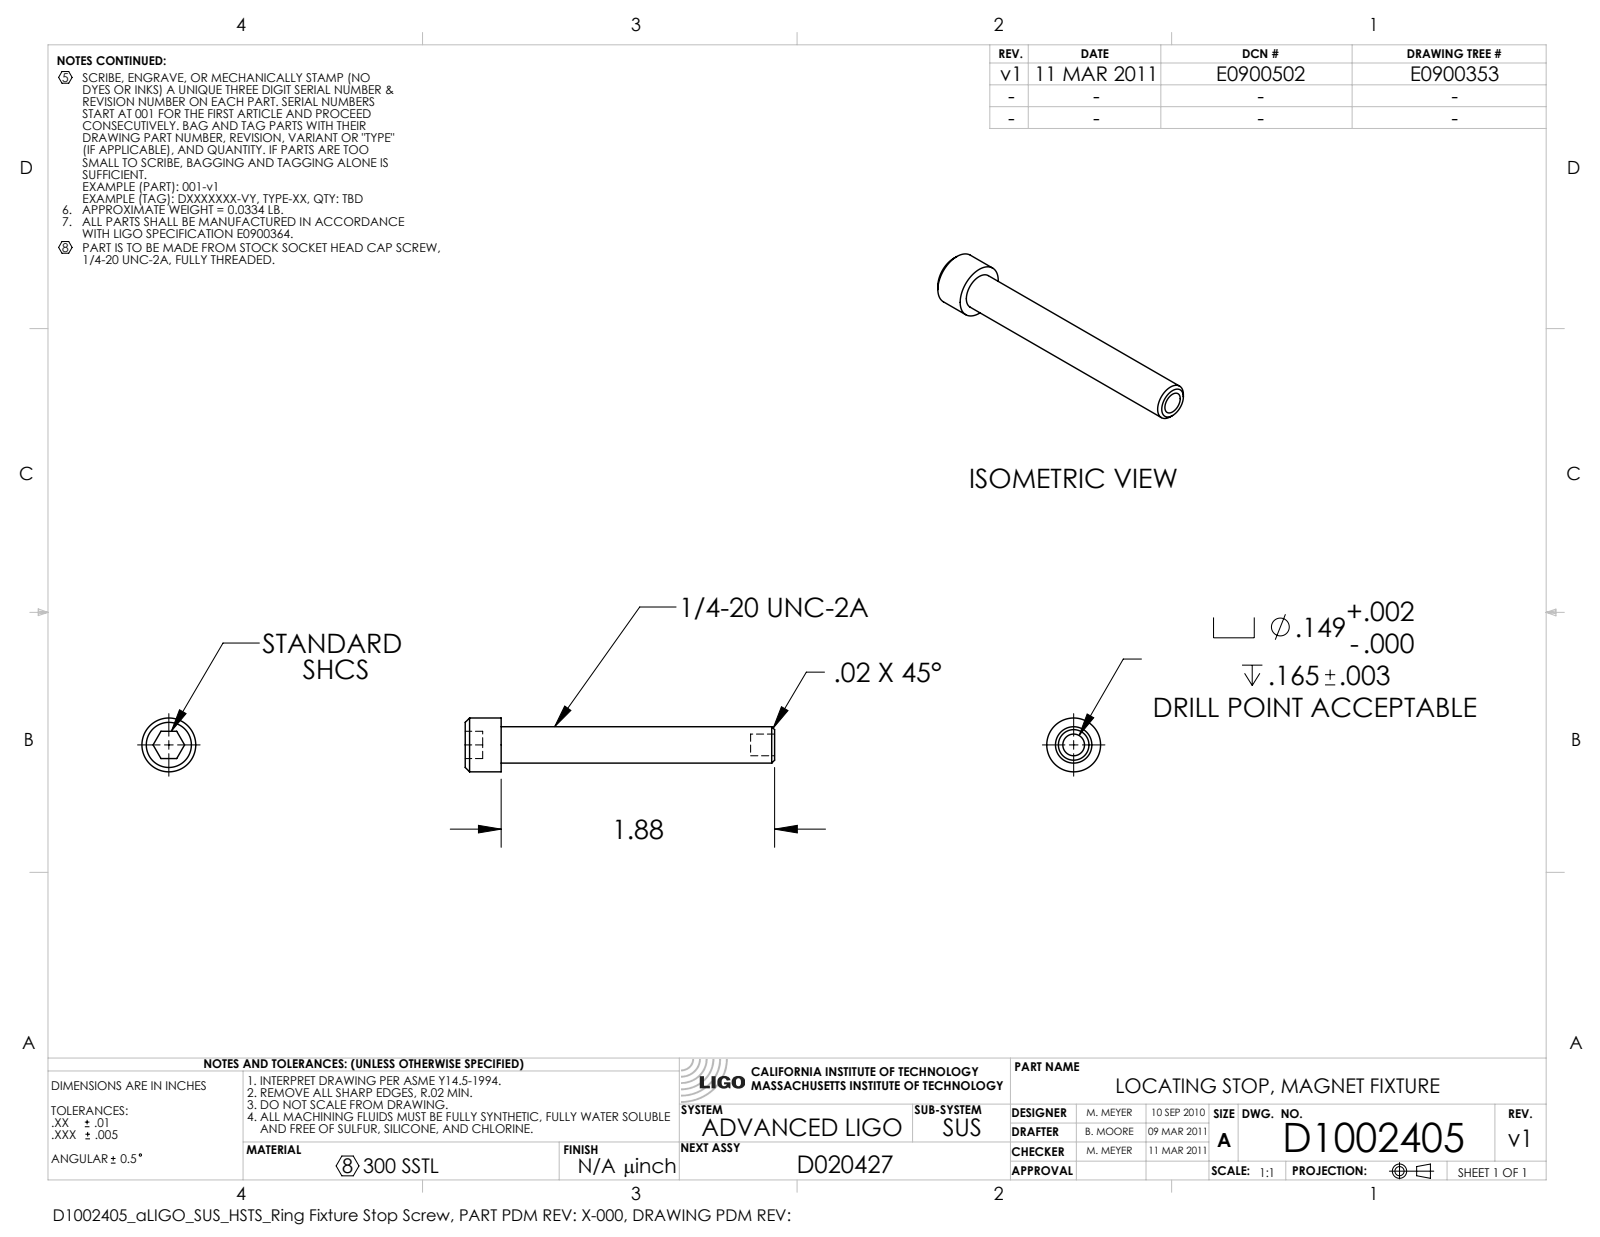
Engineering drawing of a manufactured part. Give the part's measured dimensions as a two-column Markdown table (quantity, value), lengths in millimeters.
| quantity | value |
| --- | --- |
| part name | D1002405-v1_aLIGO_SUS_HSTS_Ring Fixture Stop Screw |
| STEP written by | SolidWorks 2010 (AUTOMOTIVE_DESIGN) |
| units | millimeters |
| bodies | 1 solid, 21 faces (11 planar, 6 cylindrical, 4 other) |
| overall size | 54 × 9.4 × 9.4 |
| volume | 1 840 mm³ |
| surface area | 1 357 mm² |
| round holes (diameter × count) | 3.8 × 1 |
| round bosses / shafts (diameter × count) | 9.4 × 1, 6.4 × 1 |
| main face-to-face distances | 6.3, 4.7, 3.2, 3, 43.6, 46.8, 49.8, 4.2, 47.8, 51 |
